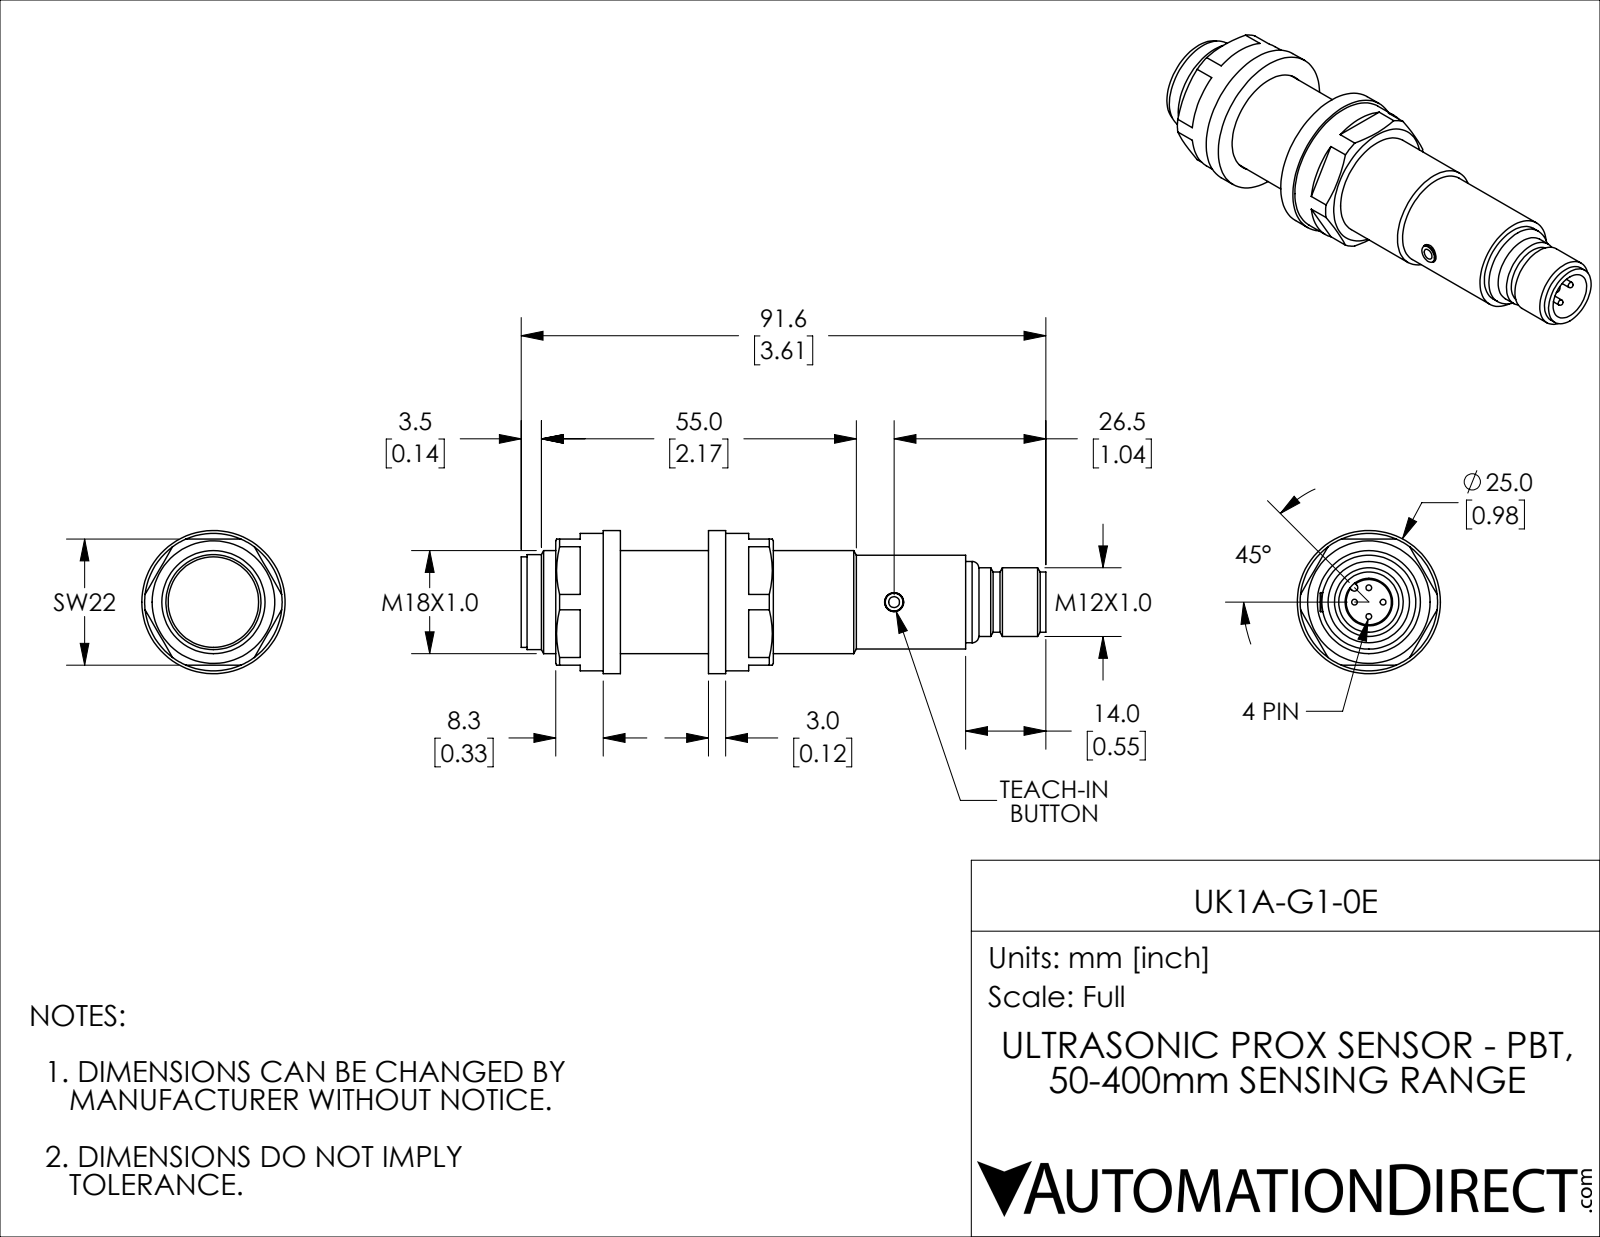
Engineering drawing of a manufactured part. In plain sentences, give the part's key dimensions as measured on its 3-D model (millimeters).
The part is named "UK1A-G1-0E". Its 3-D file was written by "SolidWorks 2018 (AUTOMOTIVE_DESIGN)". It is 6 solids with 123 faces: 43 planar, 49 cylindrical and 31 other. Overall it measures 91.6 by 25 by 25 millimeters. Its volume is 24 200 cubic millimeters and its surface area 10 330 square millimeters. Round holes: 1 of diameter 3.3, 1 of diameter 8.3, 1 of diameter 18, 1 of diameter 18.2. Round bosses or shafts: 4 of diameter 1, 1 of diameter 25, 1 of diameter 24, 1 of diameter 16.6, 1 of diameter 16.4, 1 of diameter 15.8, 1 of diameter 14.2, 1 of diameter 12. Partial cylindrical surfaces (rounded edges, fillets, slot ends): 1 of radius 0.6. The main face-to-face distances are 3, 18.4, 21.4, 15.4, 22, 8.3, 11.3, 26.7, 29.7, 14.3.
